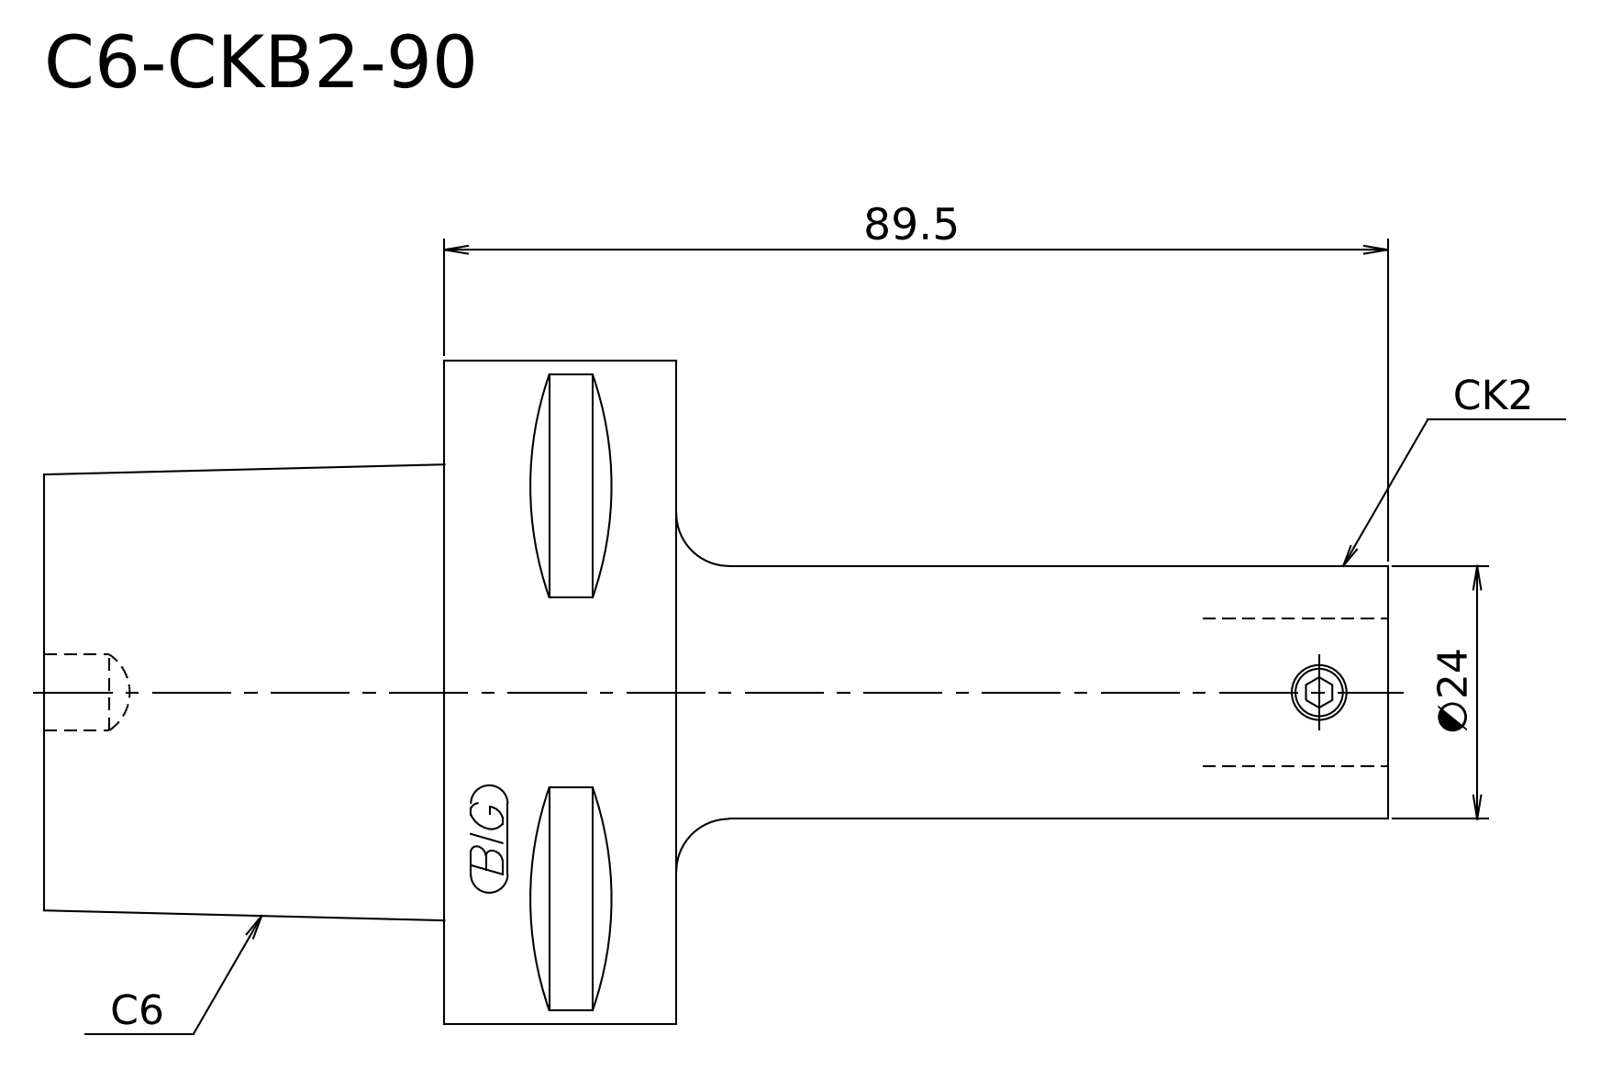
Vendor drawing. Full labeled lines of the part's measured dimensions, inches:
STEP written by: Kubotek KeyCreator V8.5.1 (14335) (CONFIG_CONTROL_DESIGN)
Units: inches
Bodies: 1 solid, 10 faces (4 planar, 2 cylindrical, 4 other)
Overall size (bounding box): 5.02 × 2.48 × 2.48
Volume: 9.454 in³ · Surface area: 31.8 in²
Round bosses / shafts (diameter × count): ⌀2.48 ×1, ⌀0.945 ×1
Main face-to-face distances: 0.866, 2.362, 1.496, 2.657, 3.524, 5.02
